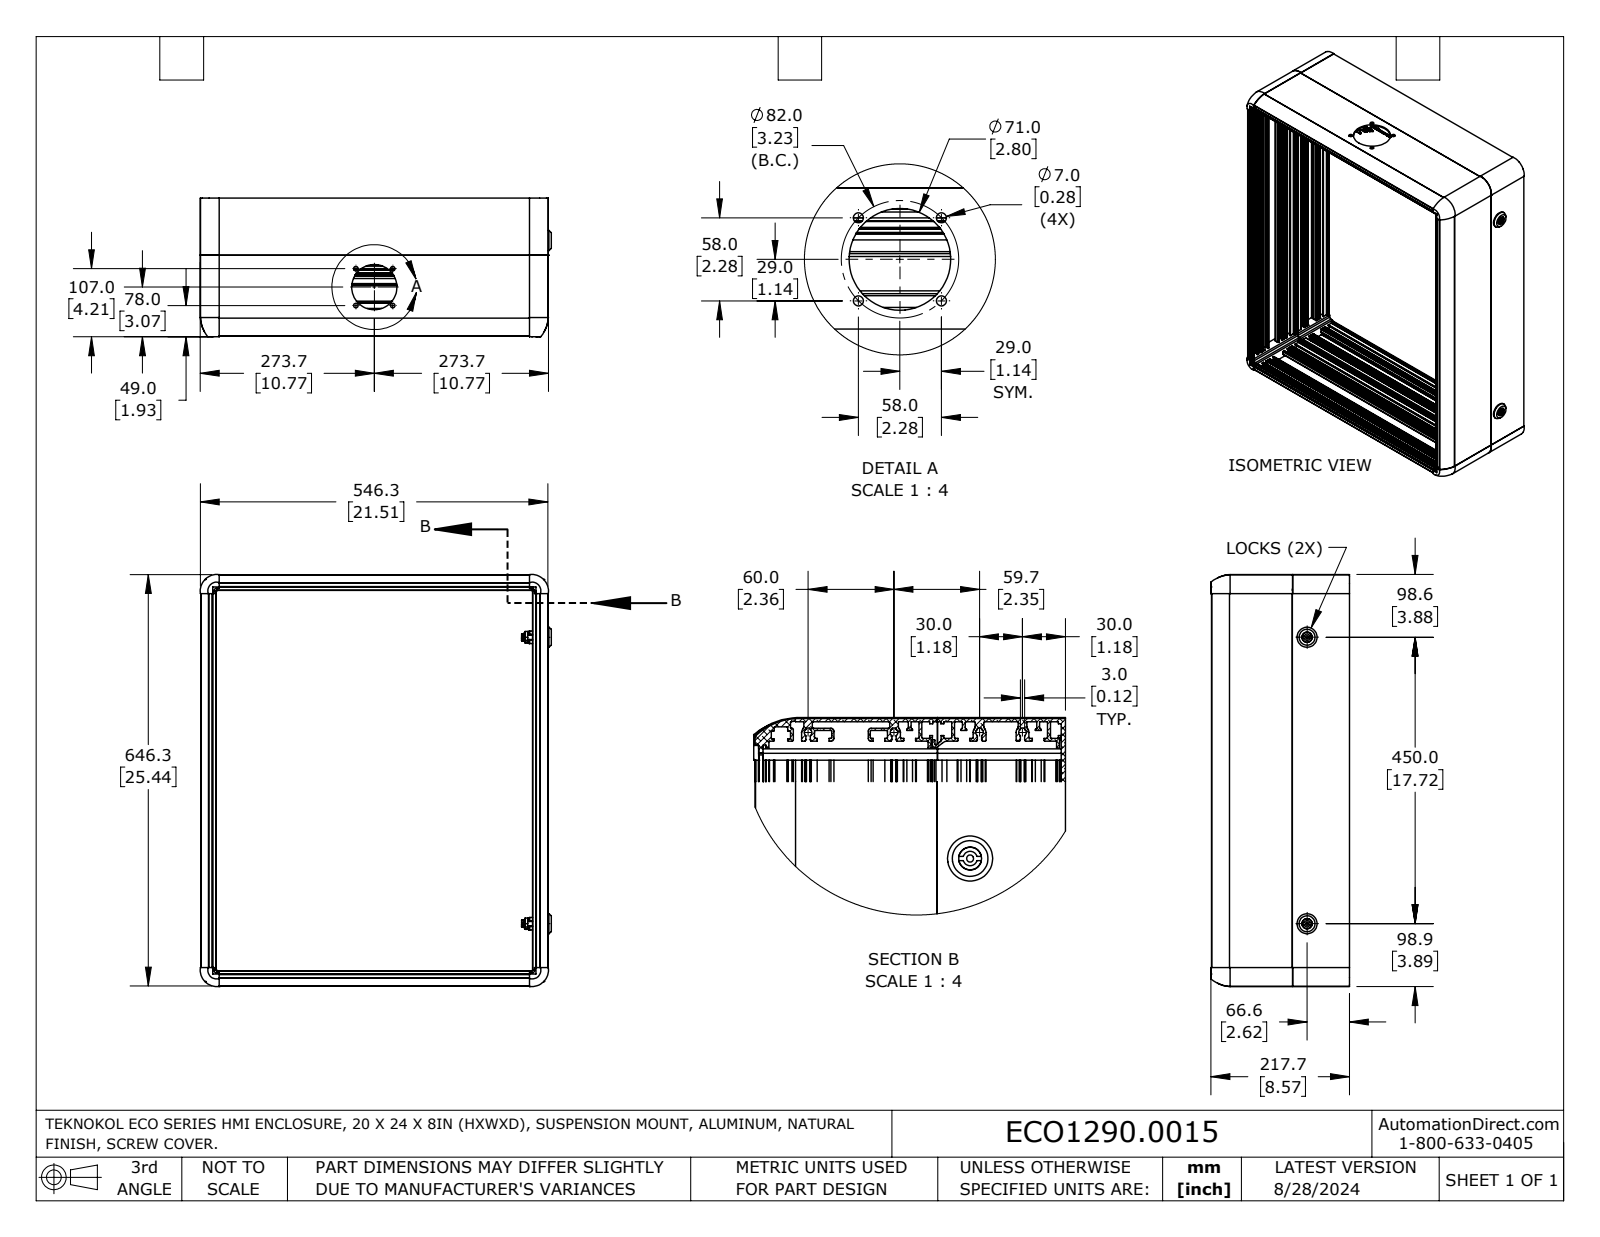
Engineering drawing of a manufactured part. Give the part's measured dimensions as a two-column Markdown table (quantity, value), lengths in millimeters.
| quantity | value |
| --- | --- |
| part name | ECO.1290.0015(500x600)_REV1 |
| STEP written by | SolidWorks 2023 (AUTOMOTIVE_DESIGN) |
| units | millimeters |
| bodies | 28 solids, 2467 faces (1295 planar, 939 cylindrical, 233 other) |
| overall size | 647.5 × 552 × 217.8 |
| volume | 4 367 000 mm³ |
| surface area | 3 055 000 mm² |
| round holes (diameter × count) | 7 × 6, 5.2 × 4, 5 × 2, 6 × 2, 6 × 2, 10 × 2, 12.1 × 2, 16 × 2, 71 × 1 |
| round bosses / shafts (diameter × count) | 9.5 × 4, 31.5 × 2, 15.8 × 2, 14.8 × 2, 13.5 × 2, 13 × 2, 12.9 × 2, 9.8 × 2 |
| partial cylindrical surfaces (radius × count) | 0.5 × 383, 1 × 76, 2 × 50, 0.2 × 48, 0.3 × 24, 0.4 × 20, 4.5 × 18, 3.3 × 17 |
| main face-to-face distances | 3, 2.3, 543.3, 2, 643.3, 13.5, 15.7, 545.6, 7.5, 645.6 |
| hole center spacings | 16.9, 41, 44.6, 58, 450, 30, 34.1, 82 |
